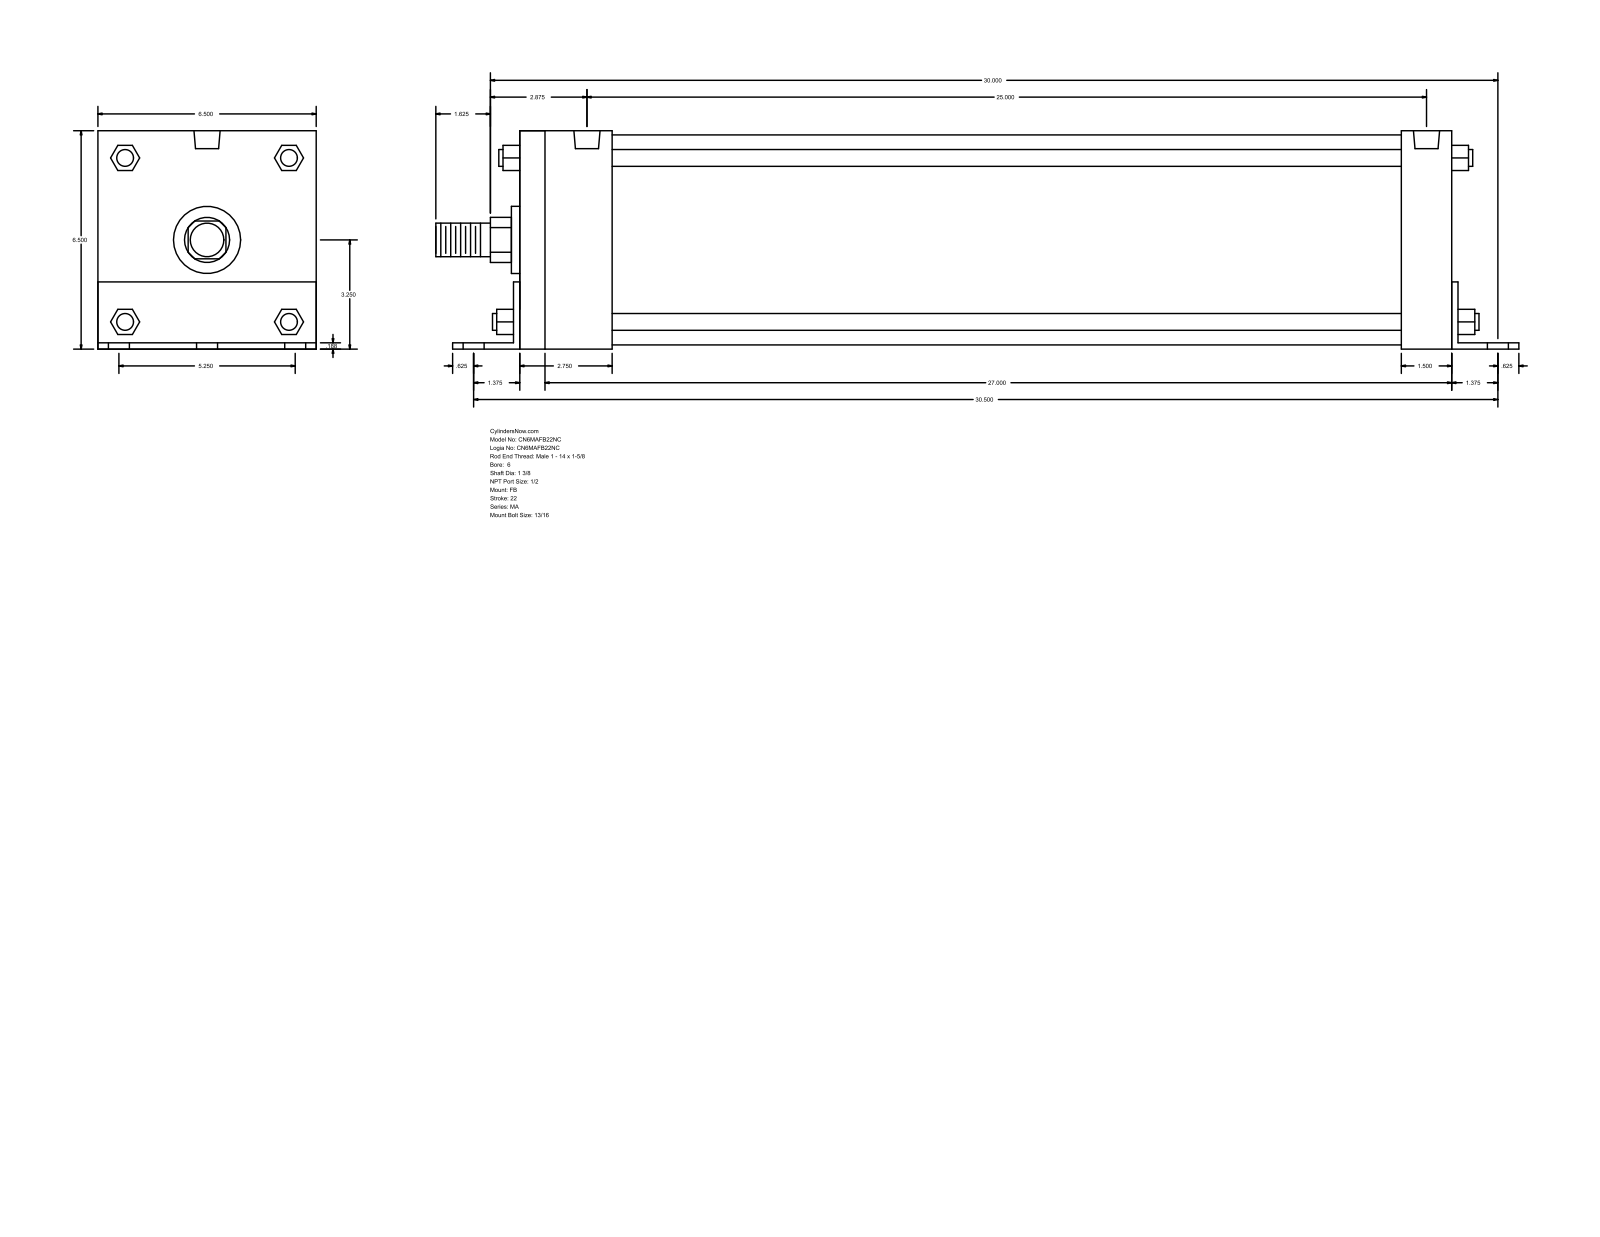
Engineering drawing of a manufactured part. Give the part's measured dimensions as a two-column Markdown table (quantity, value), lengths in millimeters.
| quantity | value |
| --- | --- |
| part name | MA_FB__0600_1.375 |
| STEP written by | GSSL Pune (CONFIG_CONTROL_DESIGN) |
| units | millimeters |
| bodies | 0 solids, 140 faces (105 planar, 35 cylindrical, 0 other) |
| overall size | 815.98 × 165.15 × 165.1 |
| round holes (diameter × count) | 20.64 × 6, 17.46 × 4, 19.77 × 2 |
| round bosses / shafts (diameter × count) | 12.7 × 4, 158.75 × 1, 50.8 × 1, 34.92 × 1, 25.4 × 1 |
| partial cylindrical surfaces (radius × count) | 17.06 × 1, 32.05 × 1 |
| main face-to-face distances | 165.1, 4.76, 701.67, 165.15, 4.71, 160.39, 4.77, 38.1, 42.86, 711.2 |
| hole center spacings | 66.67, 774.41, 771.53, 83.82, 85.78, 108.6, 133.34, 631.82 |
